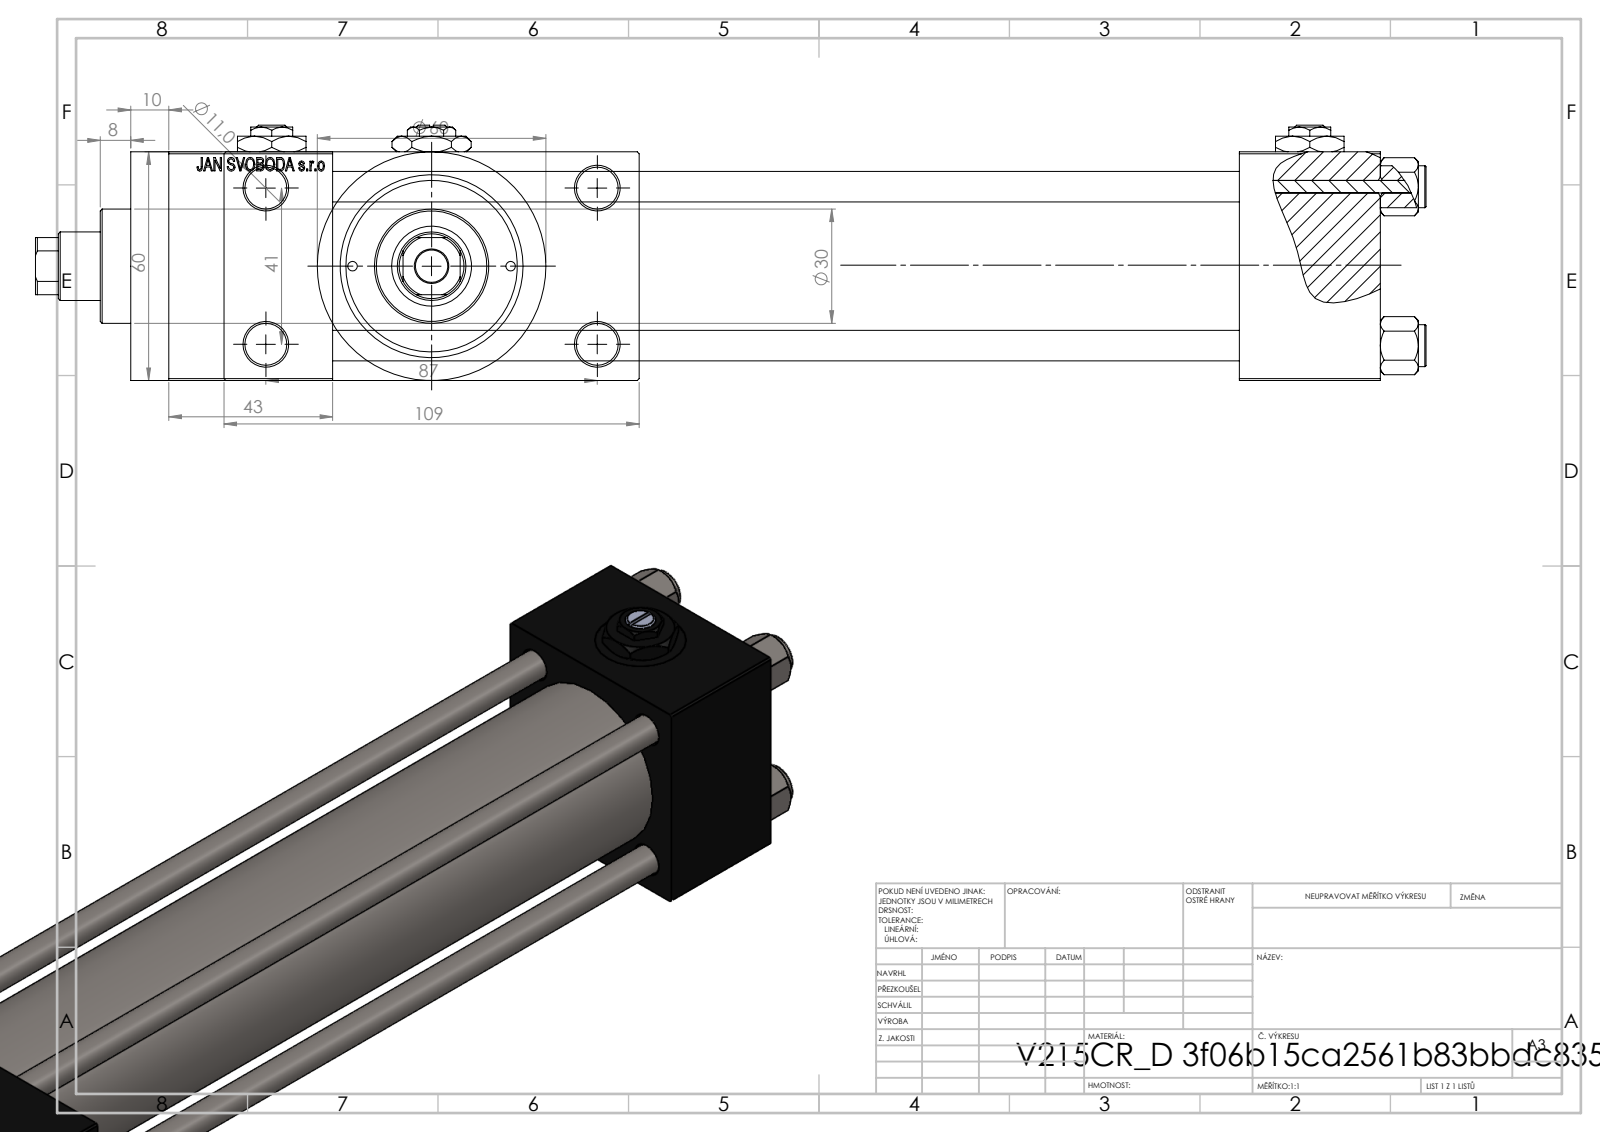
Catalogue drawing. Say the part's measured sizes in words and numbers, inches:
The part is named "V215CR_D_TYCINKA; V215_VC_A; V215CR_D_Body; V215CR_VCP_D (+2 more)". Its 3-D file was written by "SolidWorks 2019 (CONFIG_CONTROL_DESIGN)". It is 13 solids with 1214 faces: 548 planar, 104 cylindrical and 562 other. Overall it measures 14.37 by 4.291 by 2.638 inches. Its volume is 40.91 cubic inches and its surface area 311.2 square inches. Round holes: 4 of diameter 0.315, 4 of diameter 0.433, 2 of diameter 0.098, 2 of diameter 0.276, 2 of diameter 0.656, 2 of diameter 0.945, 1 of diameter 0.335, 1 of diameter 0.709, 1 of diameter 0.827, 1 of diameter 1.22, 1 of diameter 1.575, 1 of diameter 1.772. Round bosses or shafts: 4 of diameter 0.433, 1 of diameter 2.362, 1 of diameter 1.811, 1 of diameter 1.181. Partial cylindrical surfaces (rounded edges, fillets, slot ends): 1 of radius 0.335. The main face-to-face distances are 2.362, 0.965, 3.327, 9.37, 1.457, 10.827, 1.693, 12.52, 11.063, 4.291. The hole center spacings are 0.821, 0.892, 1.161, 1.206, 1.642, 1.832, 1.856, 1.893.
